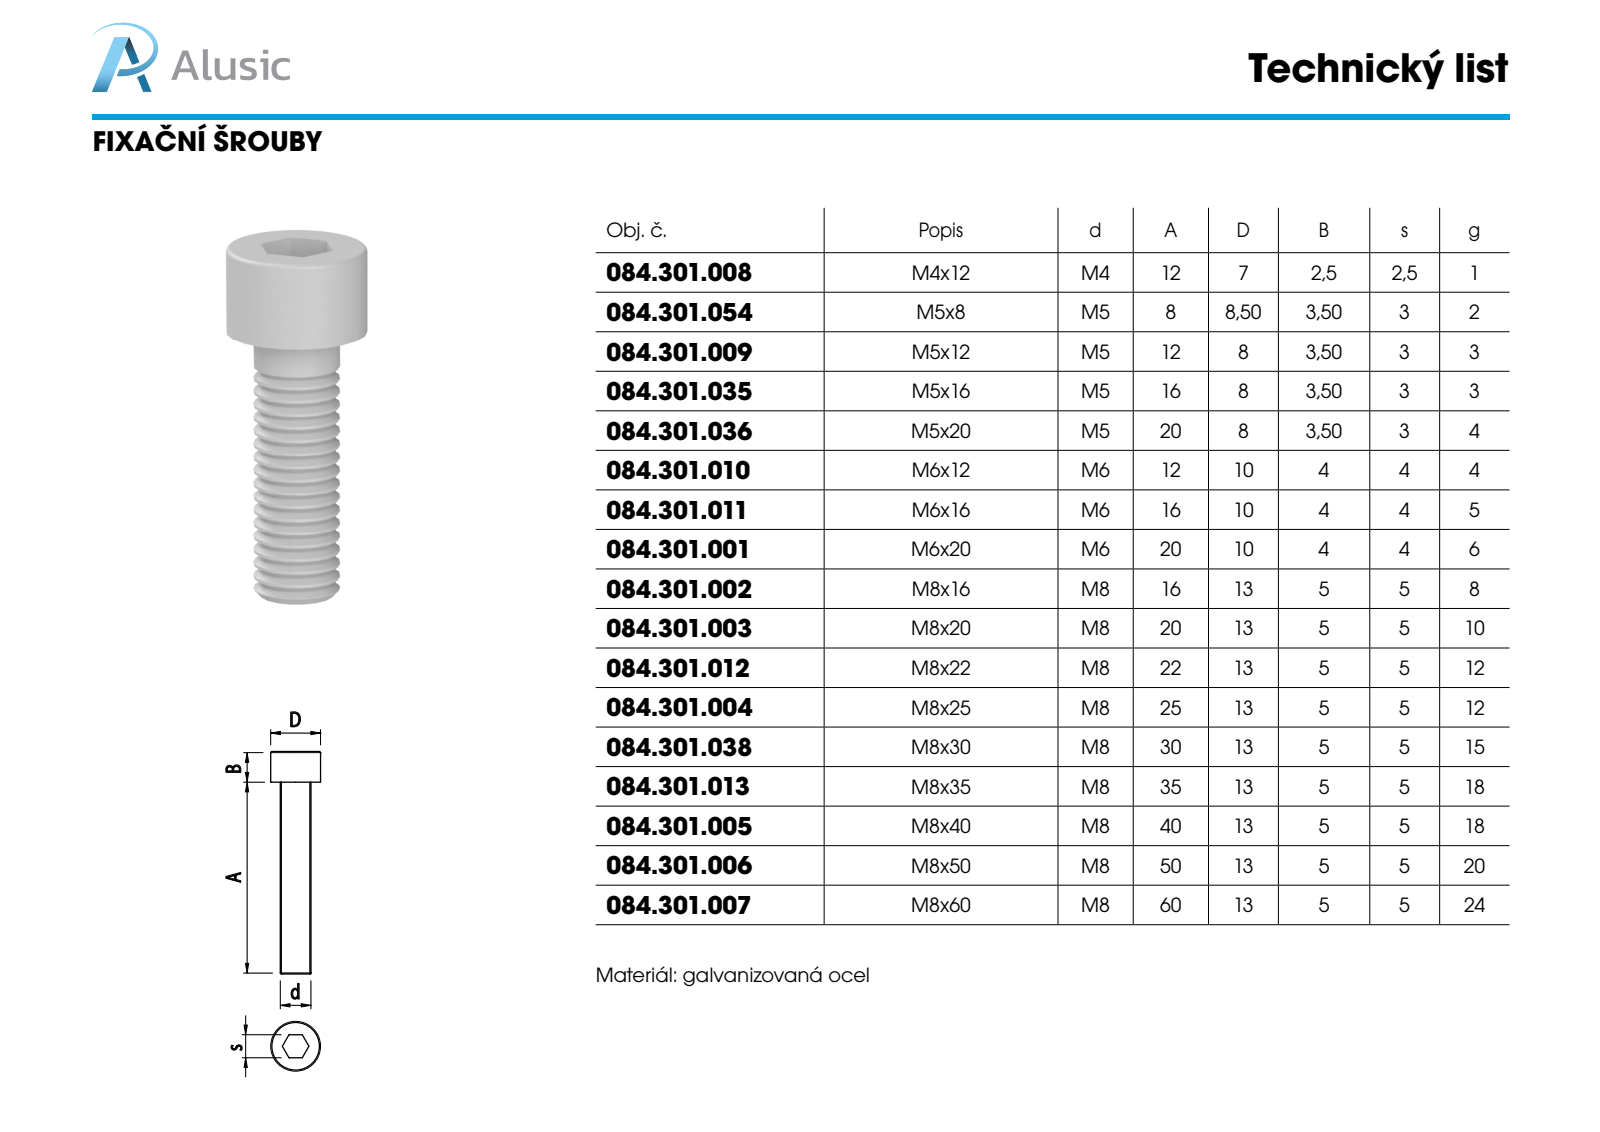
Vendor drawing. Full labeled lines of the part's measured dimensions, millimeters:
Part name (STEP PRODUCT): 084.301.008
STEP written by: SolidWorks 2012 (CONFIG_CONTROL_DESIGN)
Units: millimetres
Bodies: 1 solid, 18 faces (10 planar, 4 cylindrical, 4 other)
Overall size (bounding box): 15 × 7 × 7
Volume: 250 mm³ · Surface area: 310 mm²
Round bosses / shafts (diameter × count): ⌀7 ×1, ⌀4 ×1
Main face-to-face distances: 3, 12, 15, 13, 1, 2
